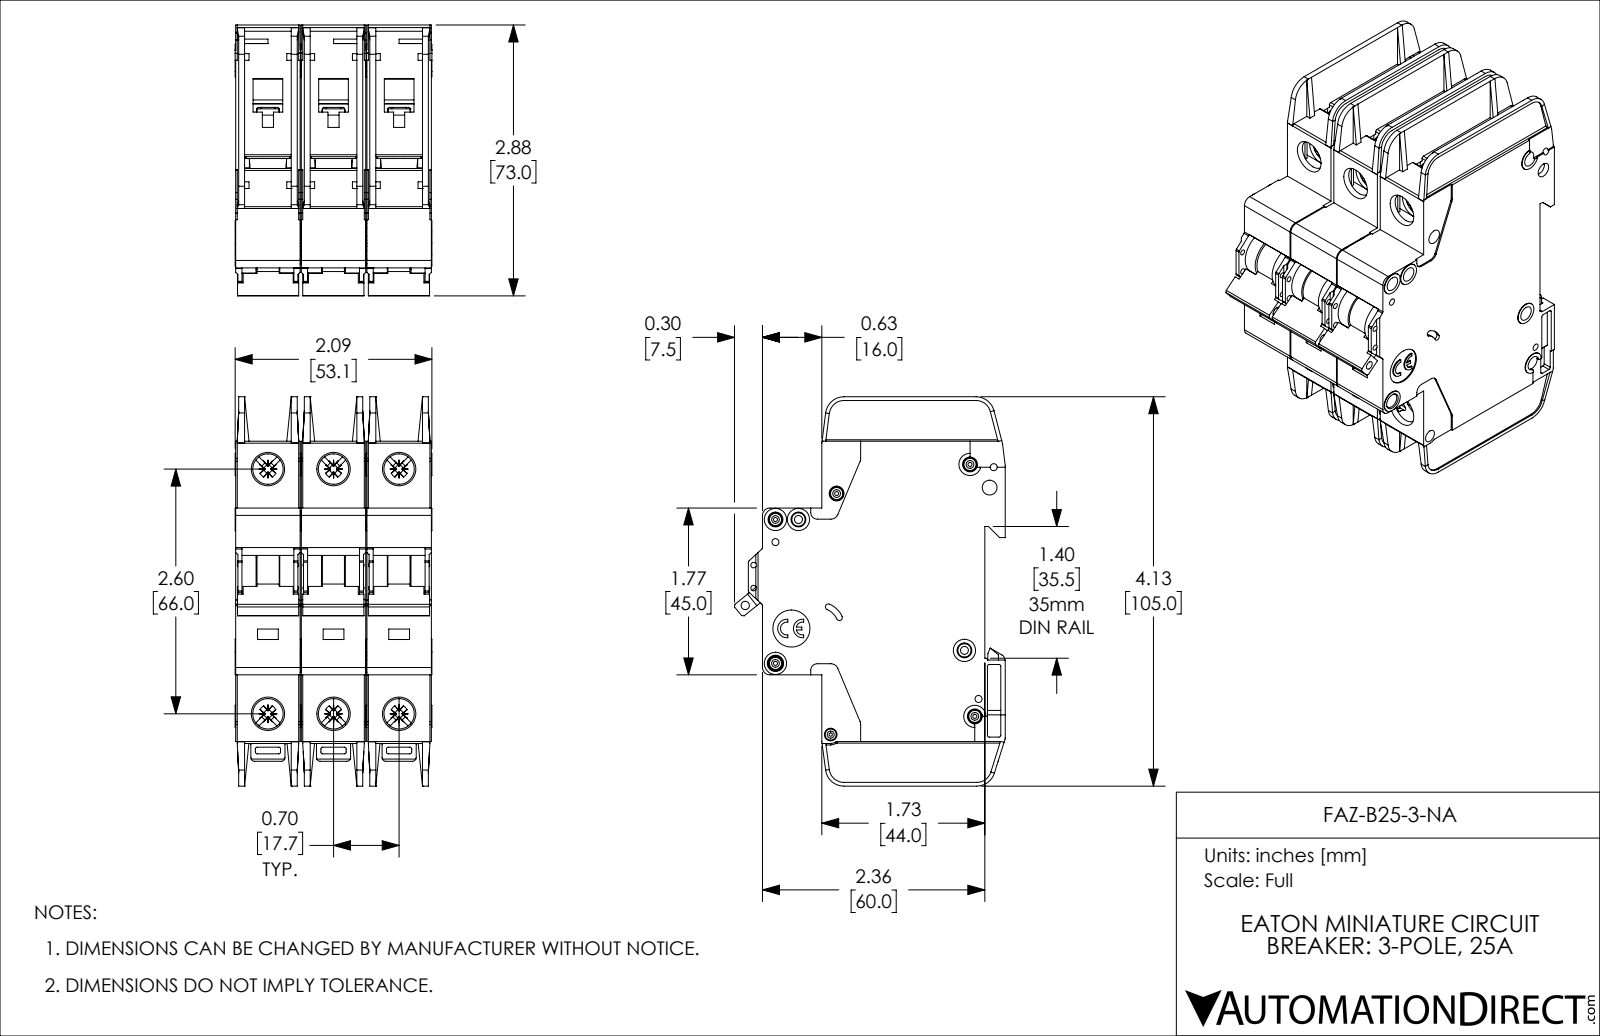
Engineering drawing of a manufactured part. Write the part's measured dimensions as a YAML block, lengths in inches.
part_name: "FAZ-B25-3-NA"
step_written_by: "SolidWorks 2019 (AUTOMOTIVE_DESIGN)"
units: inches
bodies: {solids: 3, faces: 3381, planar: 2013, cylindrical: 1071, other: 297}
overall_size: [4.134, 2.876, 2.091]
volume: 14.05
surface_area: 123
round_holes:
  - {diameter: 0.157, count: 8}
  - {diameter: 0.323, count: 6}
  - {diameter: 0.043, count: 5}
  - {diameter: 0.075, count: 4}
  - {diameter: 0.059, count: 2}
  - {diameter: 0.085, count: 2}
  - {diameter: 0.035, count: 1}
  - {diameter: 0.089, count: 1}
  - {diameter: 0.098, count: 1}
  - {diameter: 0.134, count: 1}
  - {diameter: 0.394, count: 1}
round_bosses_or_shafts:
  - {diameter: 0.13, count: 5}
  - {diameter: 0.236, count: 4}
  - {diameter: 0.118, count: 4}
  - {diameter: 0.098, count: 3}
partial_cylinders:
  - {radius: 0.02, count: 72}
  - {radius: 0.016, count: 30}
  - {radius: 0.039, count: 18}
  - {radius: 0.043, count: 12}
  - {radius: 0.079, count: 12}
  - {radius: 0.008, count: 6}
  - {radius: 0.01, count: 6}
  - {radius: 0.028, count: 6}
face_to_face_distances: [0.697, 0.047, 1.394, 0.685, 0.591, 1.382, 0.744, 0.65, 0.106, 0.094]
hole_center_spacings: [0.697, 2.69, 2.598, 0.244, 0.537, 0.87, 1.394, 2.948]
